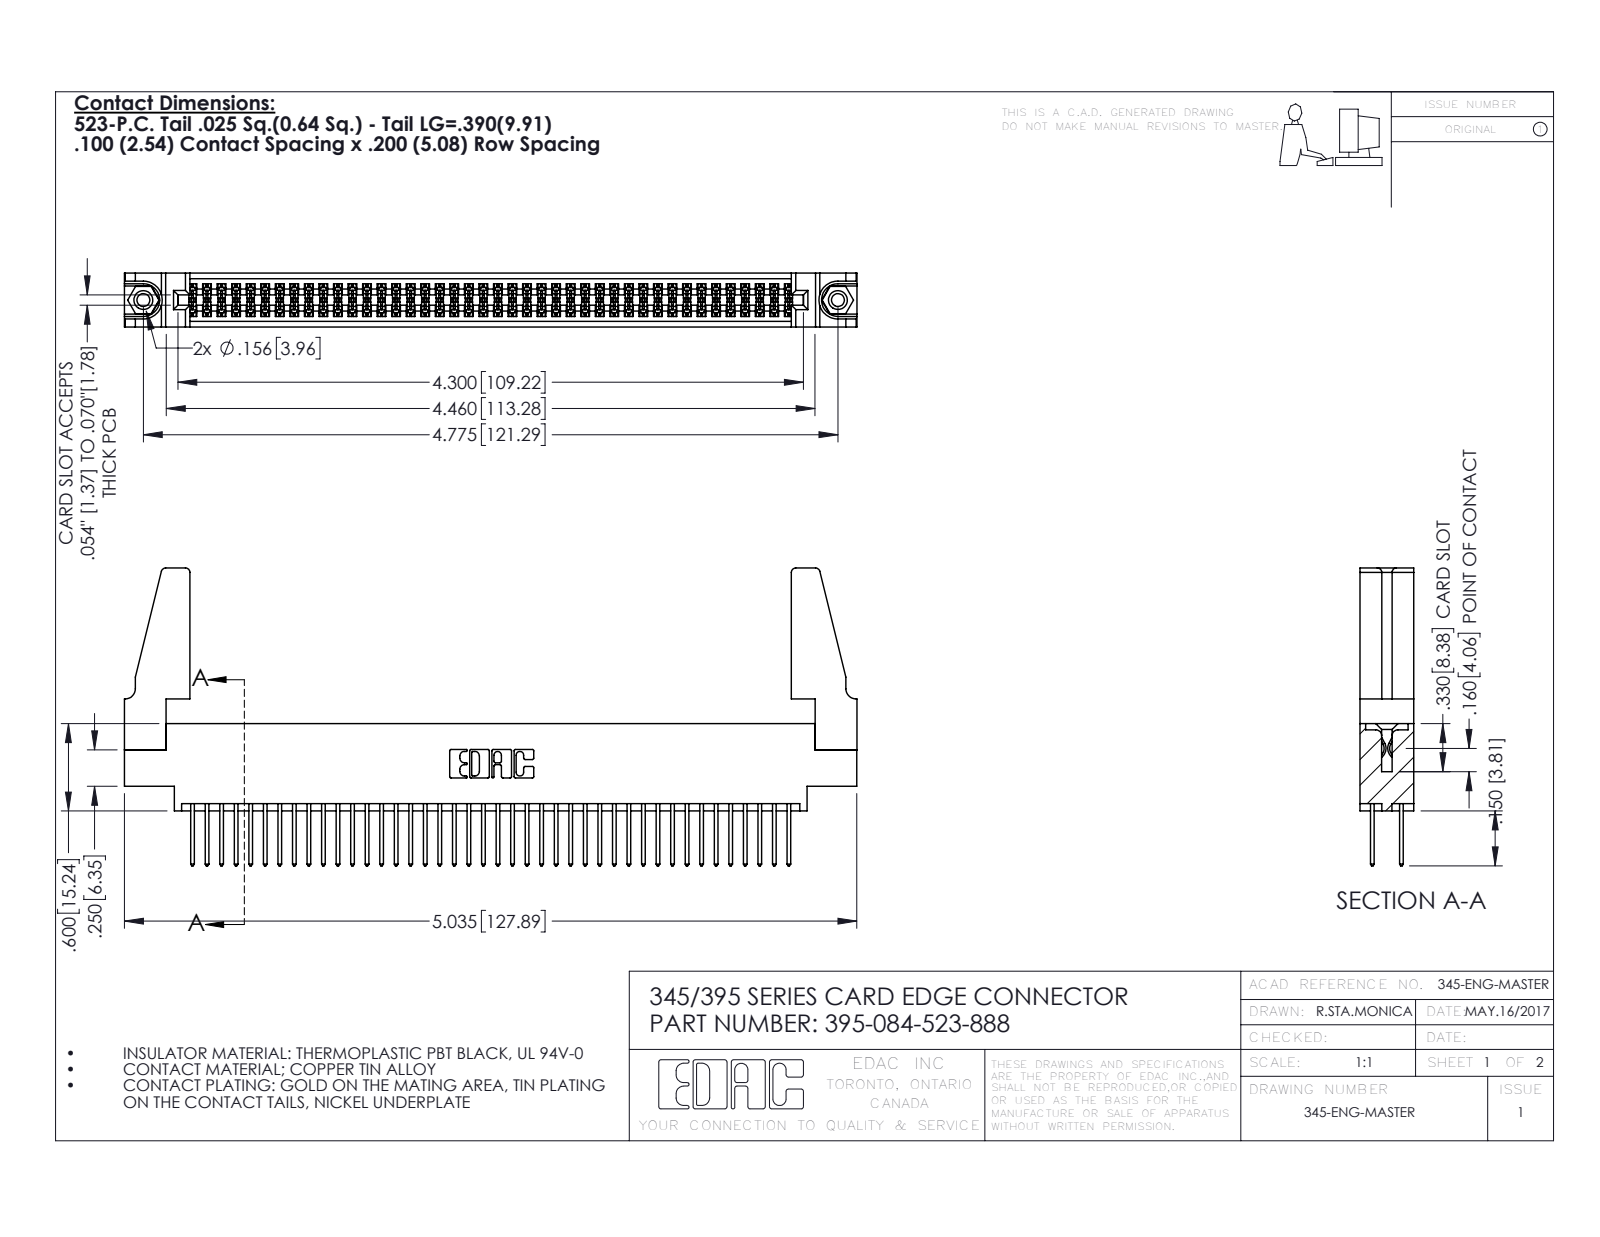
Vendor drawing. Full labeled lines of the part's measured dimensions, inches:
Part name (STEP PRODUCT): 345-220-078_345-220-088; 345 Part_0.170 Offset - 0.156 Dia-TH; 395-084-523-888; 345-250-001_345-250-001-102 (+1 more)
STEP written by: SolidWorks 2016 (CONFIG_CONTROL_DESIGN)
Units: inches
Bodies: 89 solids, 4454 faces (2928 planar, 1510 cylindrical, 16 other)
Overall size (bounding box): 5.036 × 2.047 × 0.37
Volume: 0.96 in³ · Surface area: 34.86 in²
Round holes (diameter × count): ⌀0.089 ×2, ⌀0.125 ×2, ⌀0.156 ×2, ⌀0.064 ×1
Round bosses / shafts (diameter × count): ⌀0.155 ×2
Partial cylindrical surfaces — rounded edges, fillets, slot ends (radius × count): R0.006 ×126, R0.01 ×84, R0.01 ×22, R0.03 ×8, R0.007 ×6, R0.031 ×6, R0.026 ×3, R0.014 ×2
Main face-to-face distances: 0.072, 0.298, 0.37, 0.2, 0.098, 0.272, 0.025, 0.225, 0.175, 0.149
Hole centre spacings: 0.27, 4.539, 4.775
